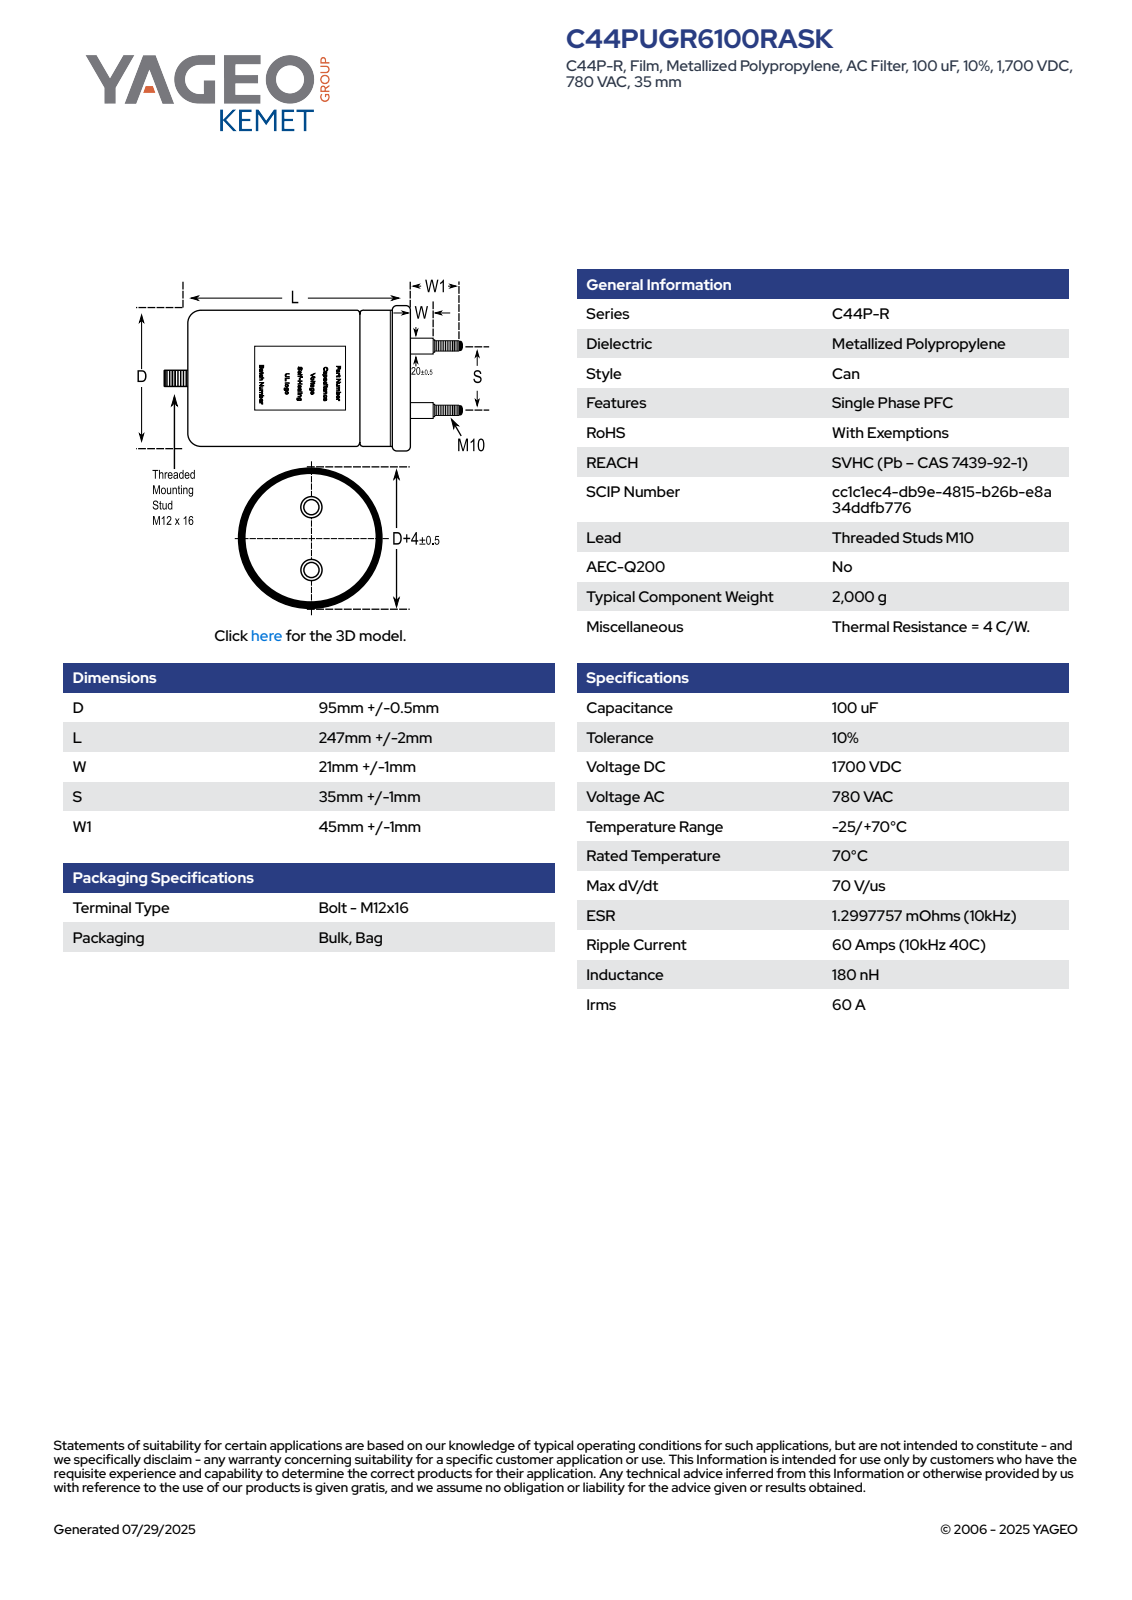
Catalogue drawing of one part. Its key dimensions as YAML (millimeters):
part_name: "CFP_C44P_95X247_D95.5L249S35"
step_written_by: "SolidWorks 2014 (AUTOMOTIVE_DESIGN)"
units: millimeters
bodies: {solids: 1, faces: 105, planar: 32, cylindrical: 36, other: 37}
overall_size: [311, 100, 100]
volume: 1807000
surface_area: 94495
round_bosses_or_shafts:
  - {diameter: 12, count: 3}
  - {diameter: 20.5, count: 2}
  - {diameter: 10, count: 2}
  - {diameter: 100, count: 1}
  - {diameter: 95.5, count: 1}
partial_cylinders:
  - {radius: 47.76, count: 1}
face_to_face_distances: [249, 270, 21, 241.01, 7.99, 28.99, 295, 53.99, 46, 25]
